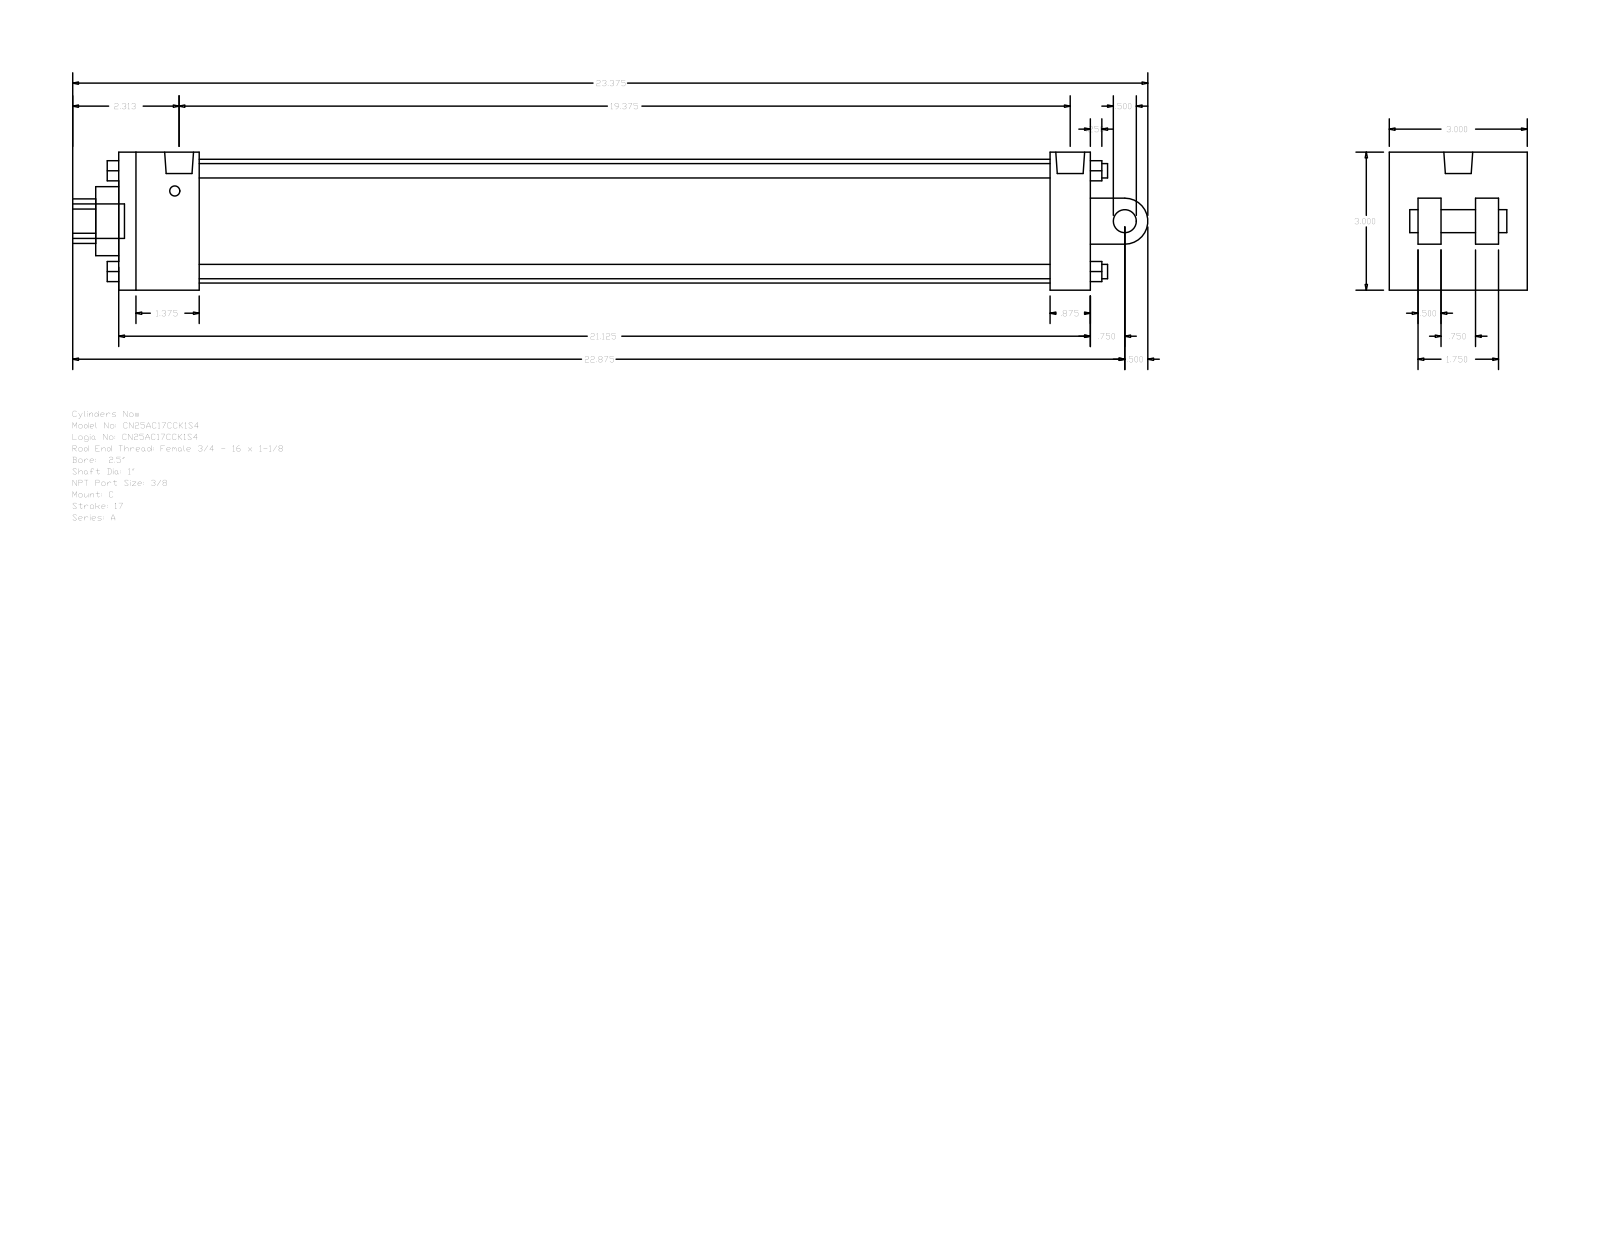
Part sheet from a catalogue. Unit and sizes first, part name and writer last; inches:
Units: inches
Overall size (bounding box): 23.375 × 3 × 3
Round holes (diameter × count): ⌀0.219 ×2, ⌀0.627 ×1, ⌀1 ×1, ⌀1.5 ×1, ⌀2.69 ×1
Round bosses / shafts (diameter × count): ⌀0.313 ×4, ⌀0.219 ×2, ⌀0.75 ×1, ⌀0.627 ×1, ⌀0.5 ×1
Partial cylindrical surfaces — rounded edges, fillets, slot ends (radius × count): R0.484 ×1, R0.5 ×1
Main face-to-face distances: 3, 21.125, 0.5, 1.75, 20.25, 18.5, 19.375, 0.875, 0.625, 1
Hole centre spacings: 0.094
Bodies: 0 solids, 135 faces (102 planar, 33 cylindrical, 0 other)
Part name (STEP PRODUCT): A_C__0250_1
STEP written by: GSSL Pune (CONFIG_CONTROL_DESIGN)
